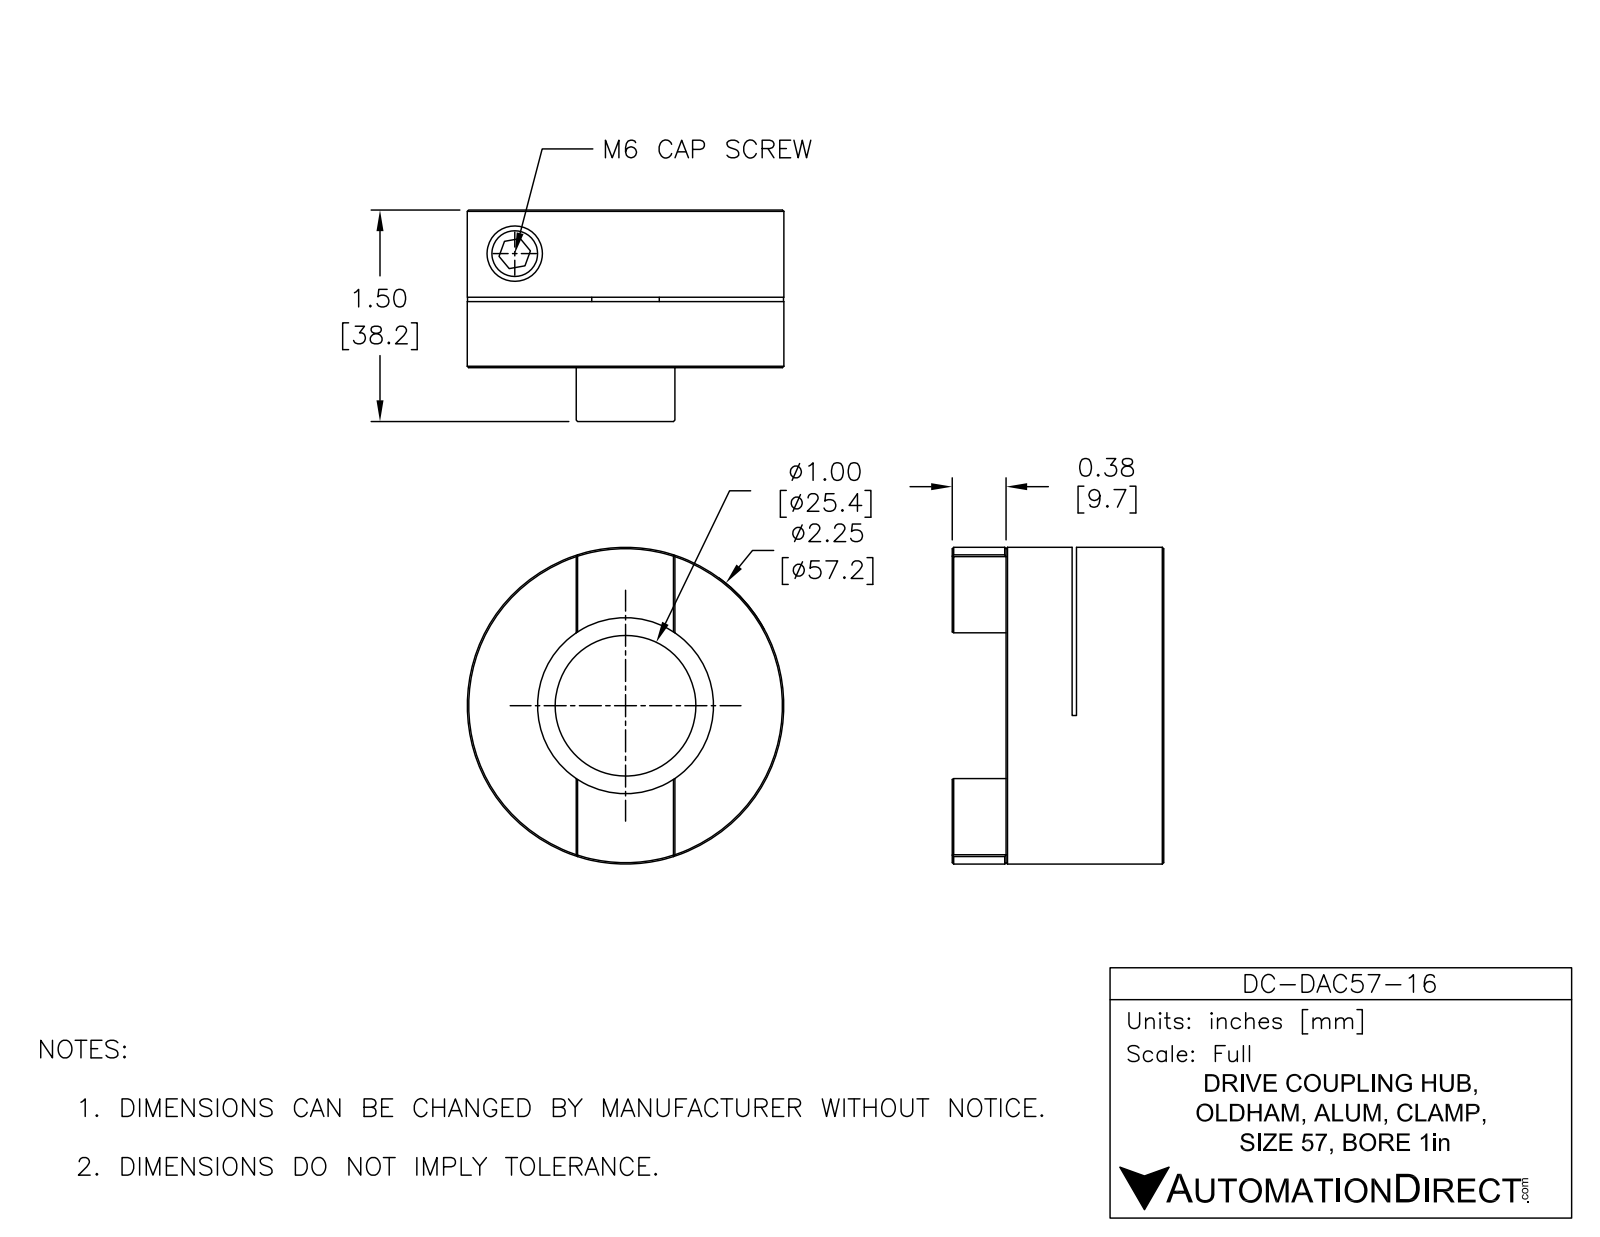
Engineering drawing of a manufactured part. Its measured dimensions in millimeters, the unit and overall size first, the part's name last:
Units: millimetres
Overall size (bounding box): 57.15 × 57.15 × 38.16
Round holes (diameter × count): ⌀6.6 ×1, ⌀11 ×1, ⌀12.7 ×1, ⌀31.75 ×1
Round bosses / shafts (diameter × count): ⌀57.15 ×1
Main face-to-face distances: 16.54, 28.45, 11.91, 15.75, 0.79, 12.7, 28, 12.25, 11.46, 0.45
Volume: 69 904 mm³ · Surface area: 16 390 mm²
Bodies: 1 solid, 55 faces (29 planar, 16 cylindrical, 10 other)
Part name (STEP PRODUCT): DC-DAC57-16
STEP written by: SolidWorks 2015 (AUTOMOTIVE_DESIGN)
